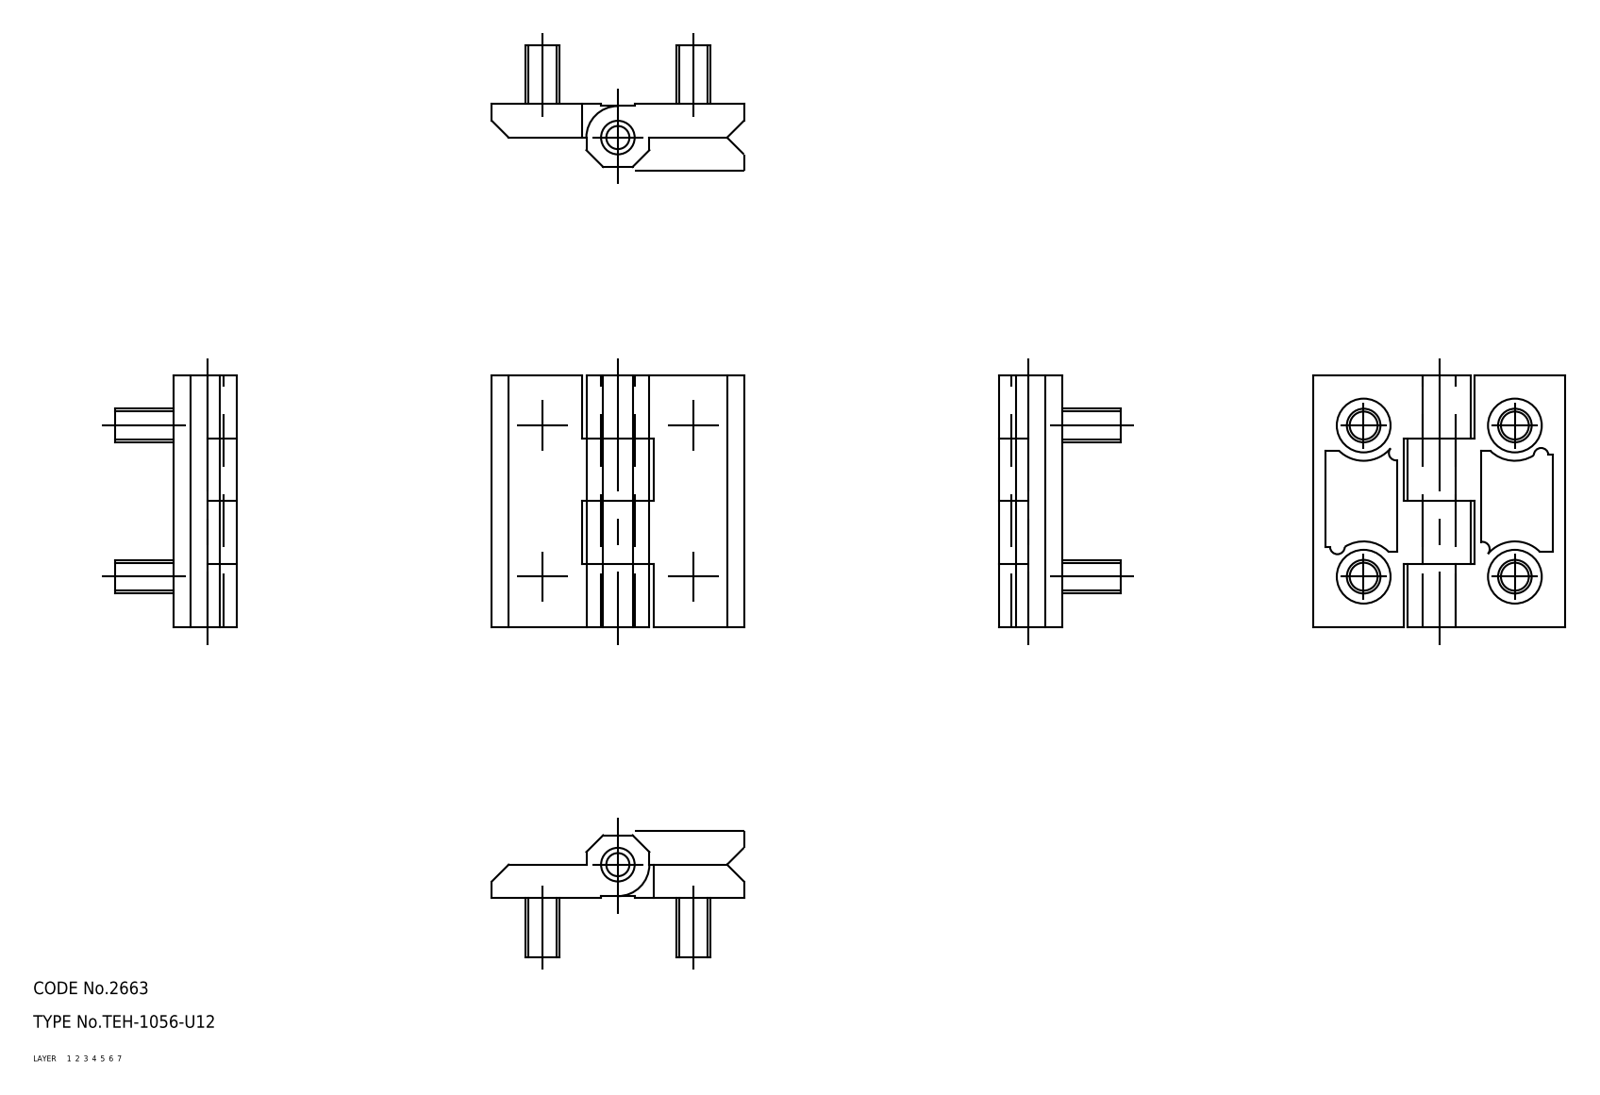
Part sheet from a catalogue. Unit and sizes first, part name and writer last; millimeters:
Units: millimetres
Overall size (bounding box): 60 × 60 × 29
Volume: 30 860 mm³ · Surface area: 17 027 mm²
Bodies: 7 solids, 118 faces (0 planar, 0 cylindrical, 118 other)
Part name (STEP PRODUCT): screw; shaft; hinge pieces_B; hinge pieces_A (+1 more)
STEP written by: CADfix (AUTOMOTIVE_DESIGN)
